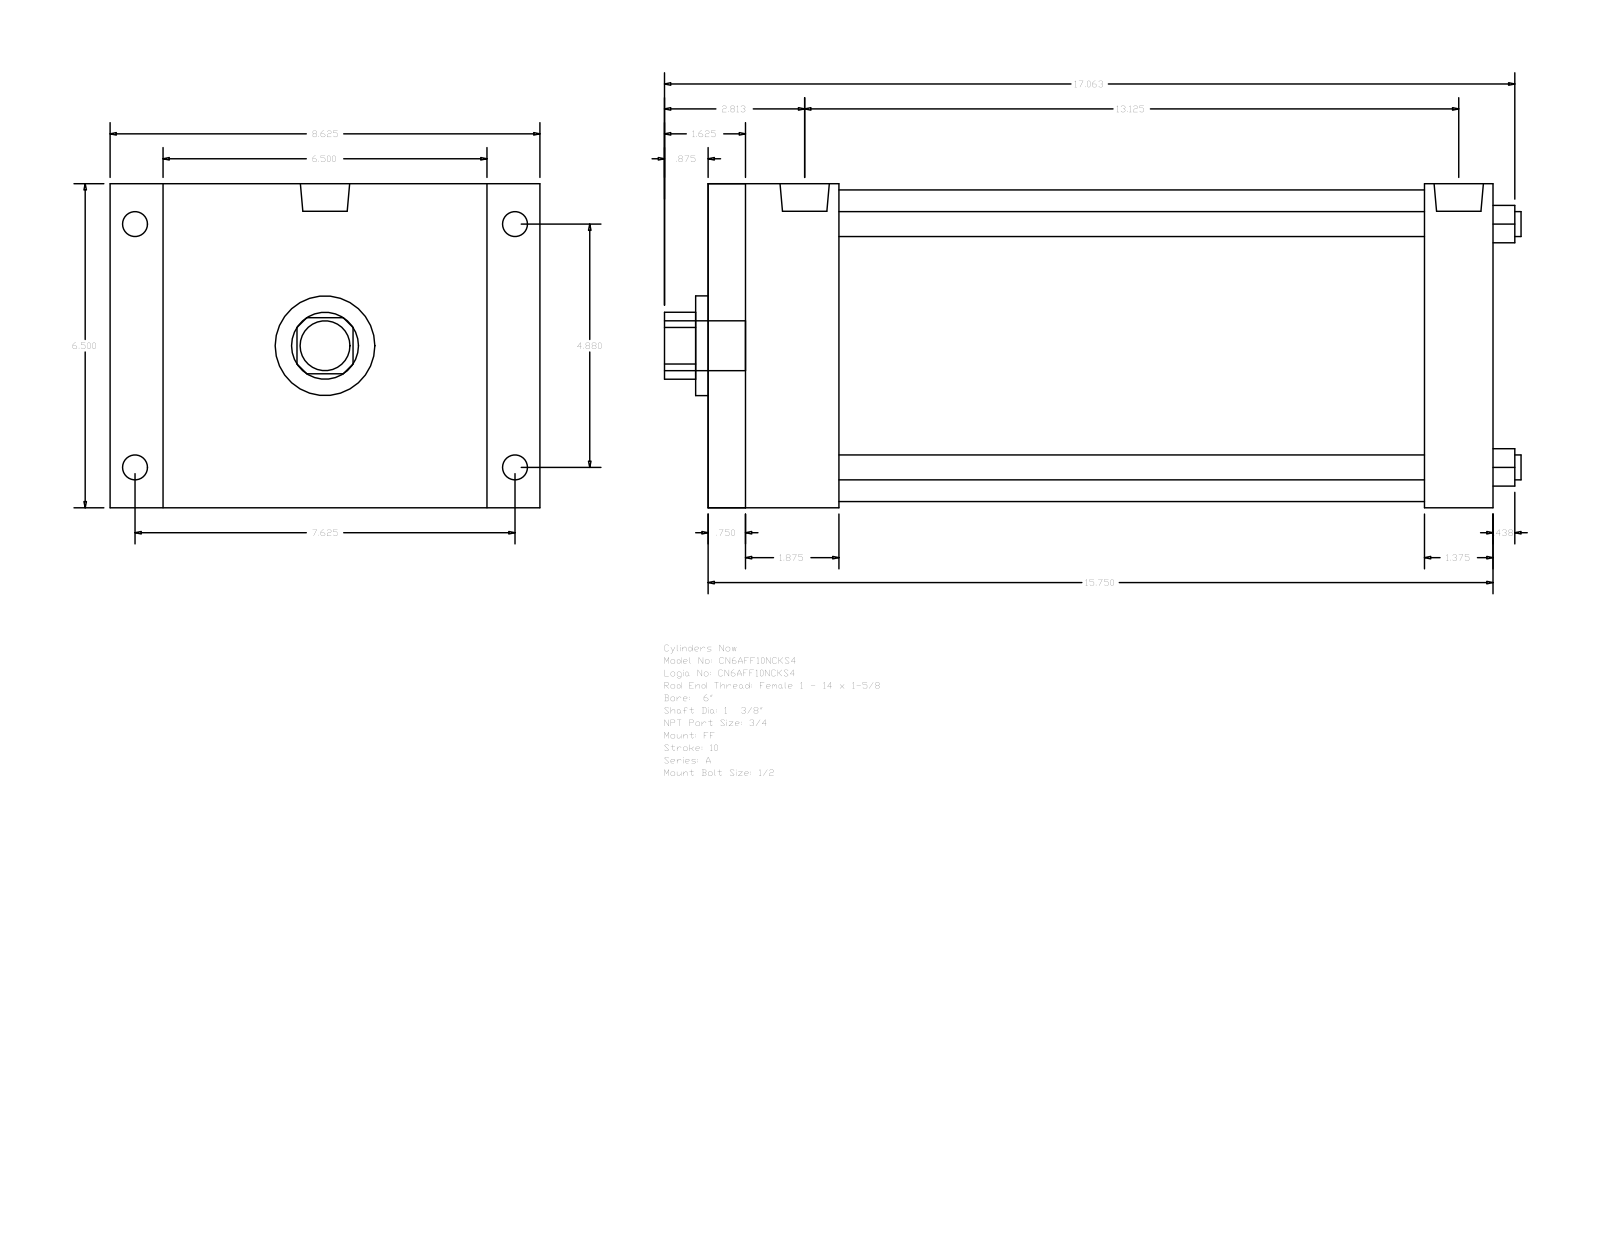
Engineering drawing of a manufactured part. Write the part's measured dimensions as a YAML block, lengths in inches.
part_name: "A_FF__0600_1.375"
step_written_by: "GSSL Pune (CONFIG_CONTROL_DESIGN)"
units: inches
bodies: {solids: 0, faces: 92, planar: 64, cylindrical: 28, other: 0}
overall_size: [17.187, 8.625, 6.5]
round_holes:
  - {diameter: 0.5, count: 4}
  - {diameter: 1.375, count: 1}
  - {diameter: 2, count: 1}
  - {diameter: 6.25, count: 1}
round_bosses_or_shafts:
  - {diameter: 0.594, count: 4}
  - {diameter: 0.5, count: 4}
  - {diameter: 0.989, count: 2}
  - {diameter: 1, count: 1}
partial_cylinders:
  - {radius: 0.672, count: 1}
face_to_face_distances: [6.5, 15.75, 0.75, 15, 2.625, 1.875, 13.125, 14.375, 13.625, 11.75]
hole_center_spacings: [3.451, 4.88, 6.902]
